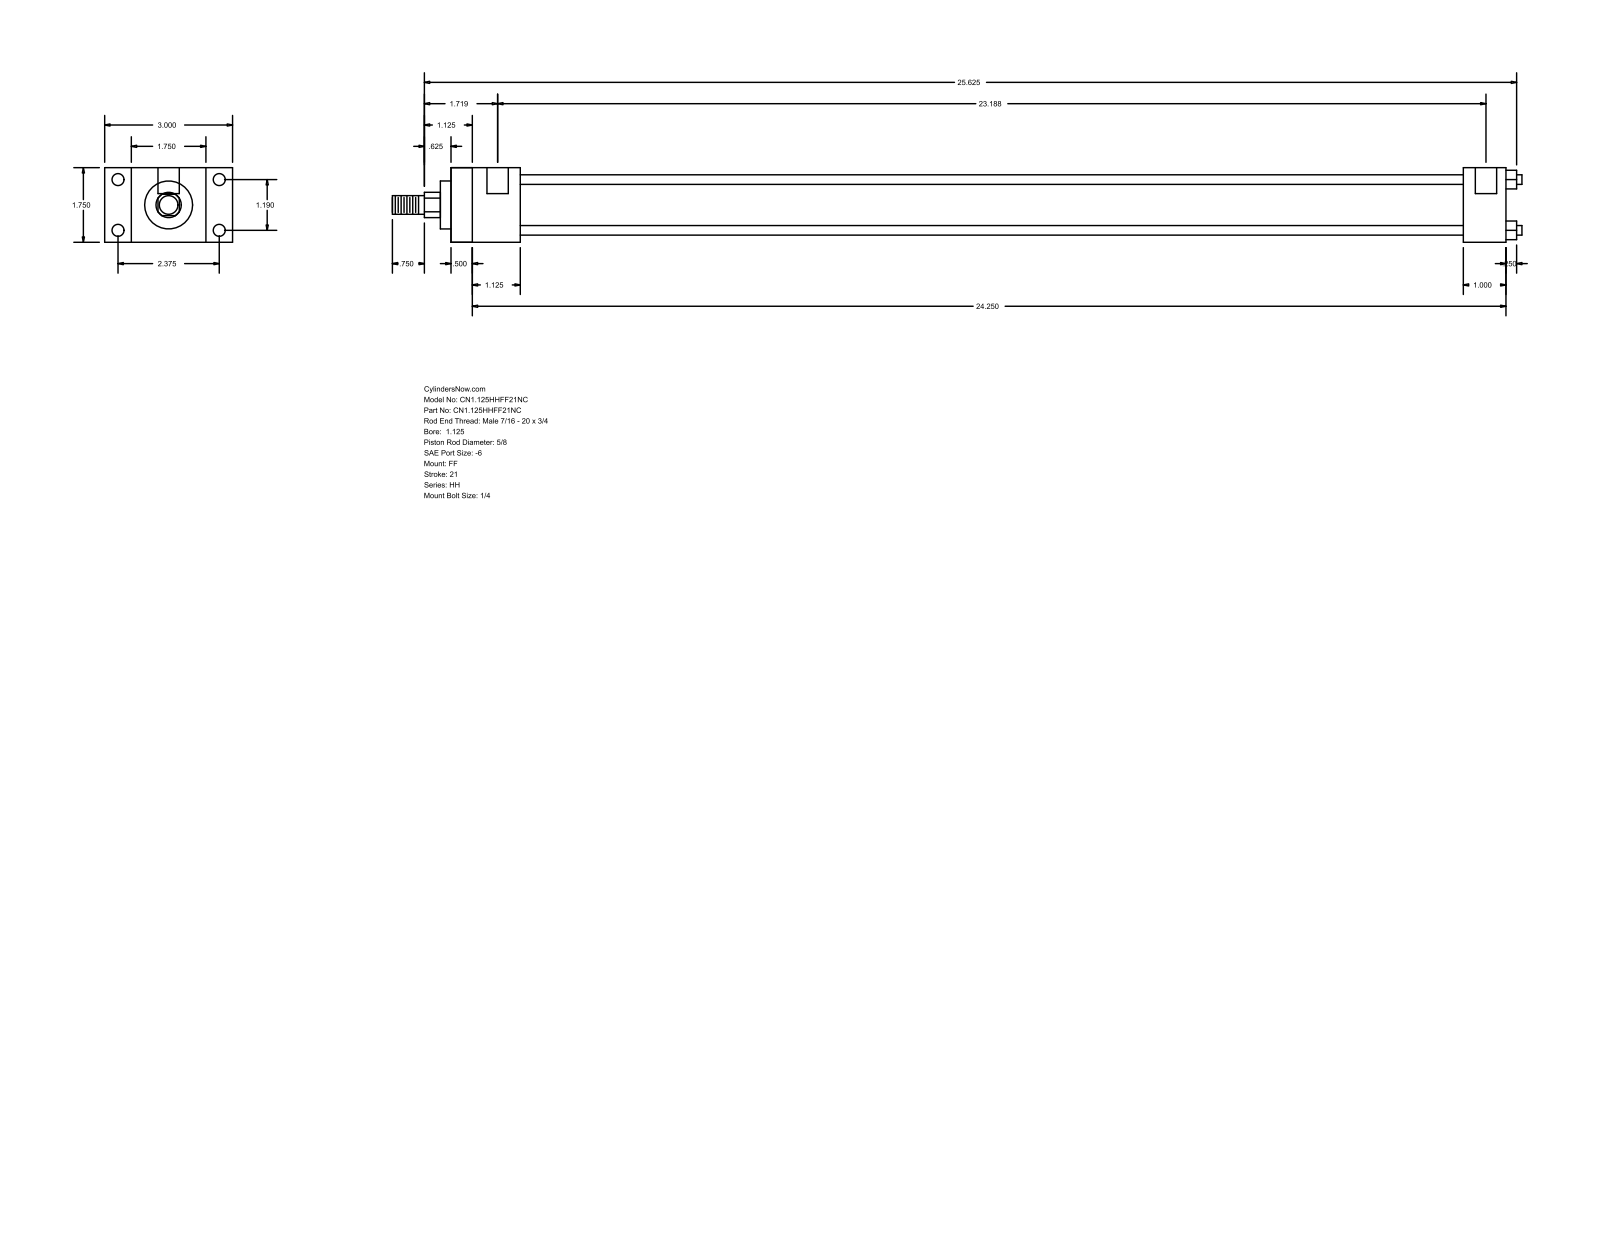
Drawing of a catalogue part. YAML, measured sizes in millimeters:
part_name: "HH_FF__0112_0.625"
step_written_by: "GSSL Pune (CONFIG_CONTROL_DESIGN)"
units: millimeters
bodies: {solids: 0, faces: 92, planar: 64, cylindrical: 28, other: 0}
overall_size: [673.1, 76.2, 44.45]
round_holes:
  - {diameter: 5.56, count: 4}
  - {diameter: 7.14, count: 4}
  - {diameter: 12.7, count: 2}
round_bosses_or_shafts:
  - {diameter: 5.71, count: 4}
  - {diameter: 34.92, count: 1}
  - {diameter: 28.57, count: 1}
  - {diameter: 15.88, count: 1}
  - {diameter: 11.11, count: 1}
partial_cylinders:
  - {radius: 7.54, count: 1}
face_to_face_distances: [44.46, 628.64, 15.87, 12.69, 615.95, 28.58, 60.33, 25.4, 41.27, 603.24]
hole_center_spacings: [30.22, 60.32, 67.47, 585.79, 3.17, 588.96]
